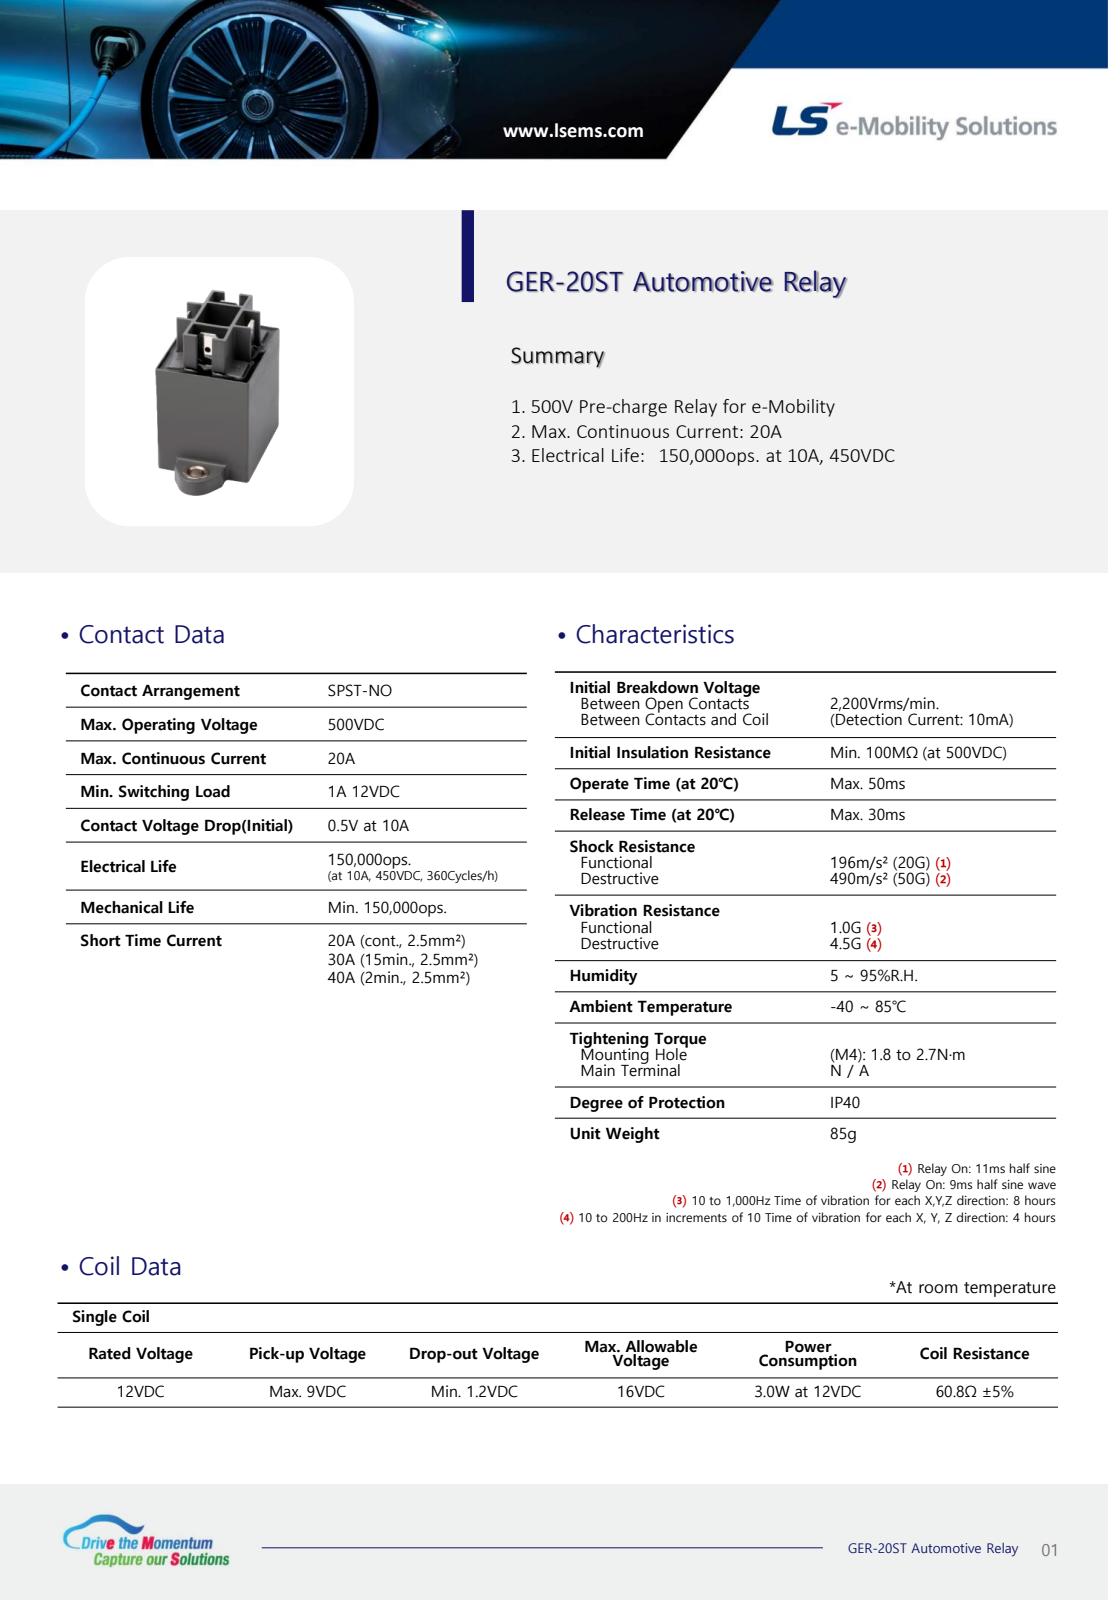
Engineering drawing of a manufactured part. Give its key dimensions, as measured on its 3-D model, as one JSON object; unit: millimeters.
{"part_name": "40010009ST_GER010-STAAPP0A01_AllCATPart", "step_written_by": "CATIA V5 STEP AP214 (AUTOMOTIVE_DESIGN)", "units": "millimeters", "bodies": {"solids": 8, "faces": 647, "planar": 406, "cylindrical": 157, "other": 84}, "overall_size": [55.8, 44.7, 28], "volume_mm3": 10667, "surface_area_mm2": 16416, "round_holes": [[2.7, 3], [4.5, 2], [6.5, 2], [7.5, 2], [1, 1], [1.3, 1], [1.7, 1]], "partial_cylinders_radius": [[0.5, 76], [1, 11], [0.8, 5], [4.75, 2], [5.4, 2], [1.6, 1]], "face_to_face_distances": [1.2, 26.8, 32.8, 28, 7.65, 19.15, 25.6, 1, 11.5, 30.2], "hole_center_spacings": [13.9, 38.12, 7.5, 22, 28, 35.61, 45]}
